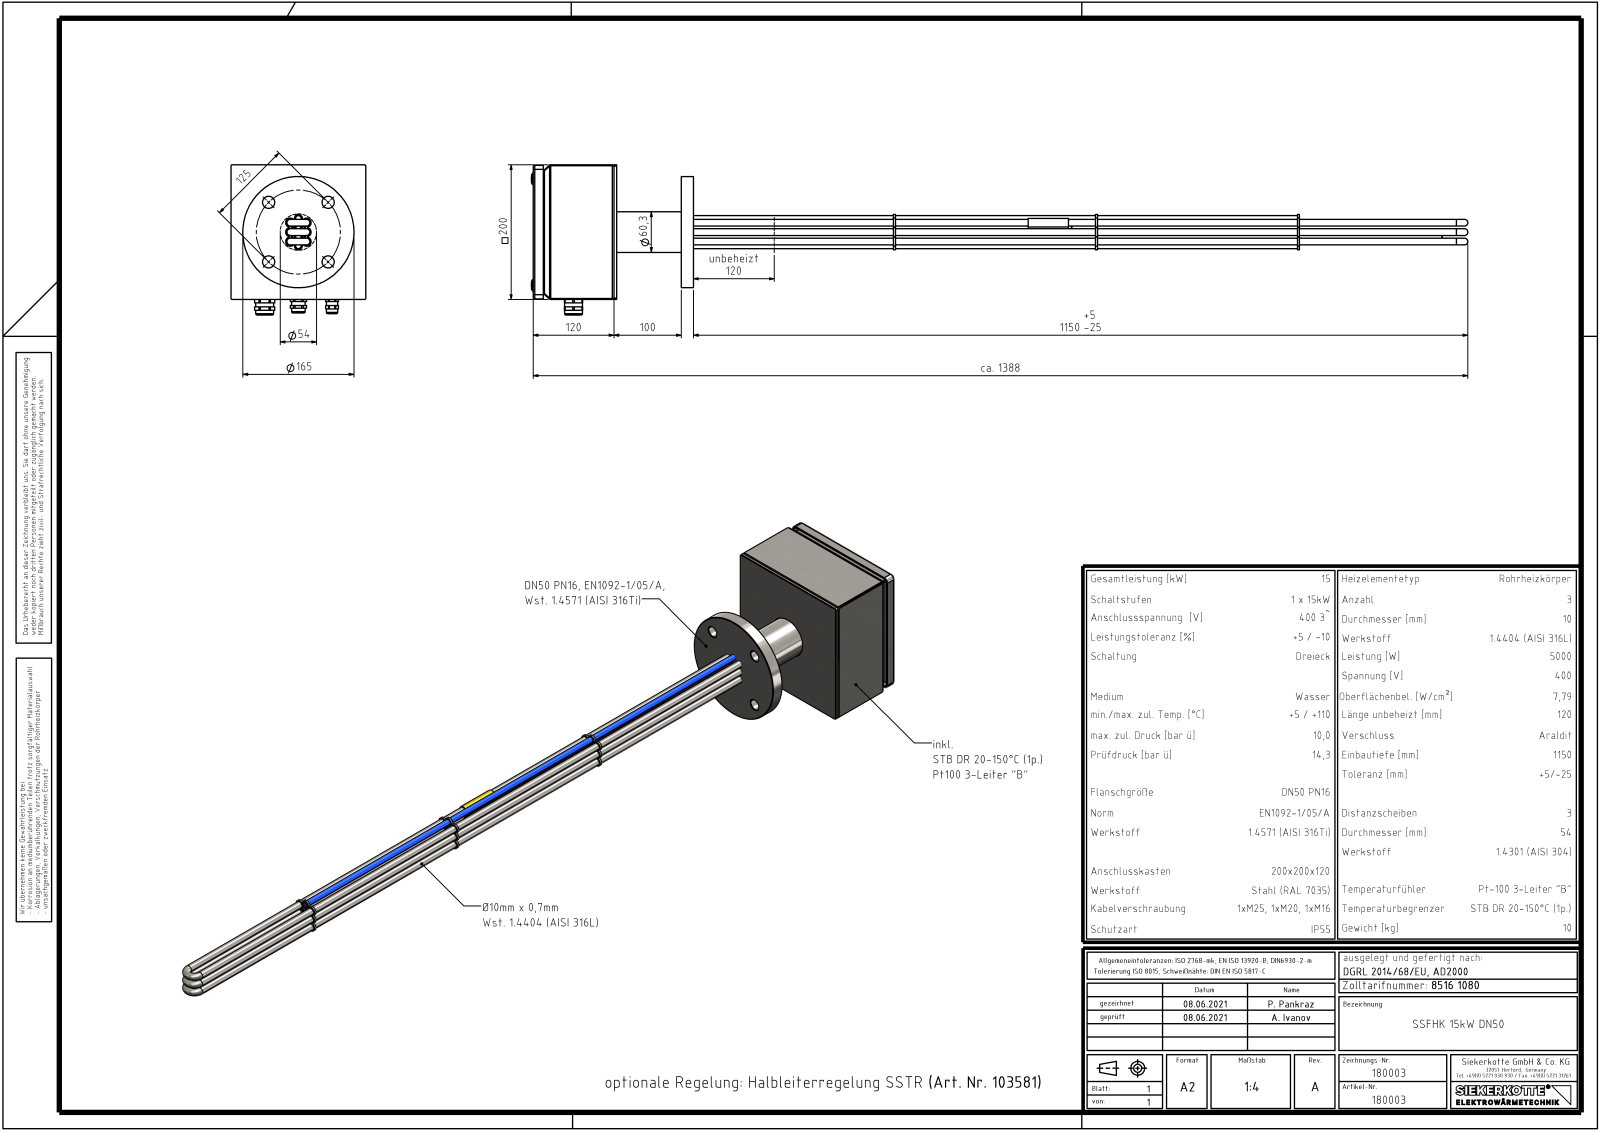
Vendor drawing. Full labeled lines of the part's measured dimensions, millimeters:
Part name (STEP PRODUCT): FSR STB^Fühlerschutzrohre_SSFHK; BODY^AK 200x200x120_Anschlusskasten_SSFHK; AK 200x200x120^Anschlusskasten_SSFHK; SCREW^AK 200x200x120_Anschlusskasten_SSFHK (+8 more)
STEP written by: SolidWorks 2021 (AUTOMOTIVE_DESIGN)
Units: millimetres
Bodies: 25 solids, 1400 faces (362 planar, 758 cylindrical, 280 other)
Overall size (bounding box): 1390.75 × 223 × 200
Volume: 1 150 000 mm³ · Surface area: 1 072 000 mm²
Round holes (diameter × count): ⌀10.2 ×10, ⌀8 ×6, ⌀10.7 ×6, ⌀5 ×4, ⌀8.4 ×4, ⌀8.7 ×4, ⌀18 ×4, ⌀8.5 ×3, ⌀7 ×2, ⌀9.2 ×2, ⌀9.7 ×2, ⌀6.2 ×1
Round bosses / shafts (diameter × count): ⌀10 ×10, ⌀8 ×6, ⌀9.4 ×4, ⌀5.3 ×4, ⌀5 ×4, ⌀4.3 ×4, ⌀2.7 ×4, ⌀11.5 ×2
Partial cylindrical surfaces — rounded edges, fillets, slot ends (radius × count): R0.5 ×54, R1.25 ×24, R2.5 ×24, R5 ×8, R2 ×6, R2.25 ×6, R6.85 ×6, R6 ×5
Main face-to-face distances: 1.25, 198.75, 118.75, 200, 4, 120, 124, 197.5, 122.75, 118
Hole centre spacings: 128.01, 129.25, 159, 1.41, 13.89, 14, 18.44, 27.78
